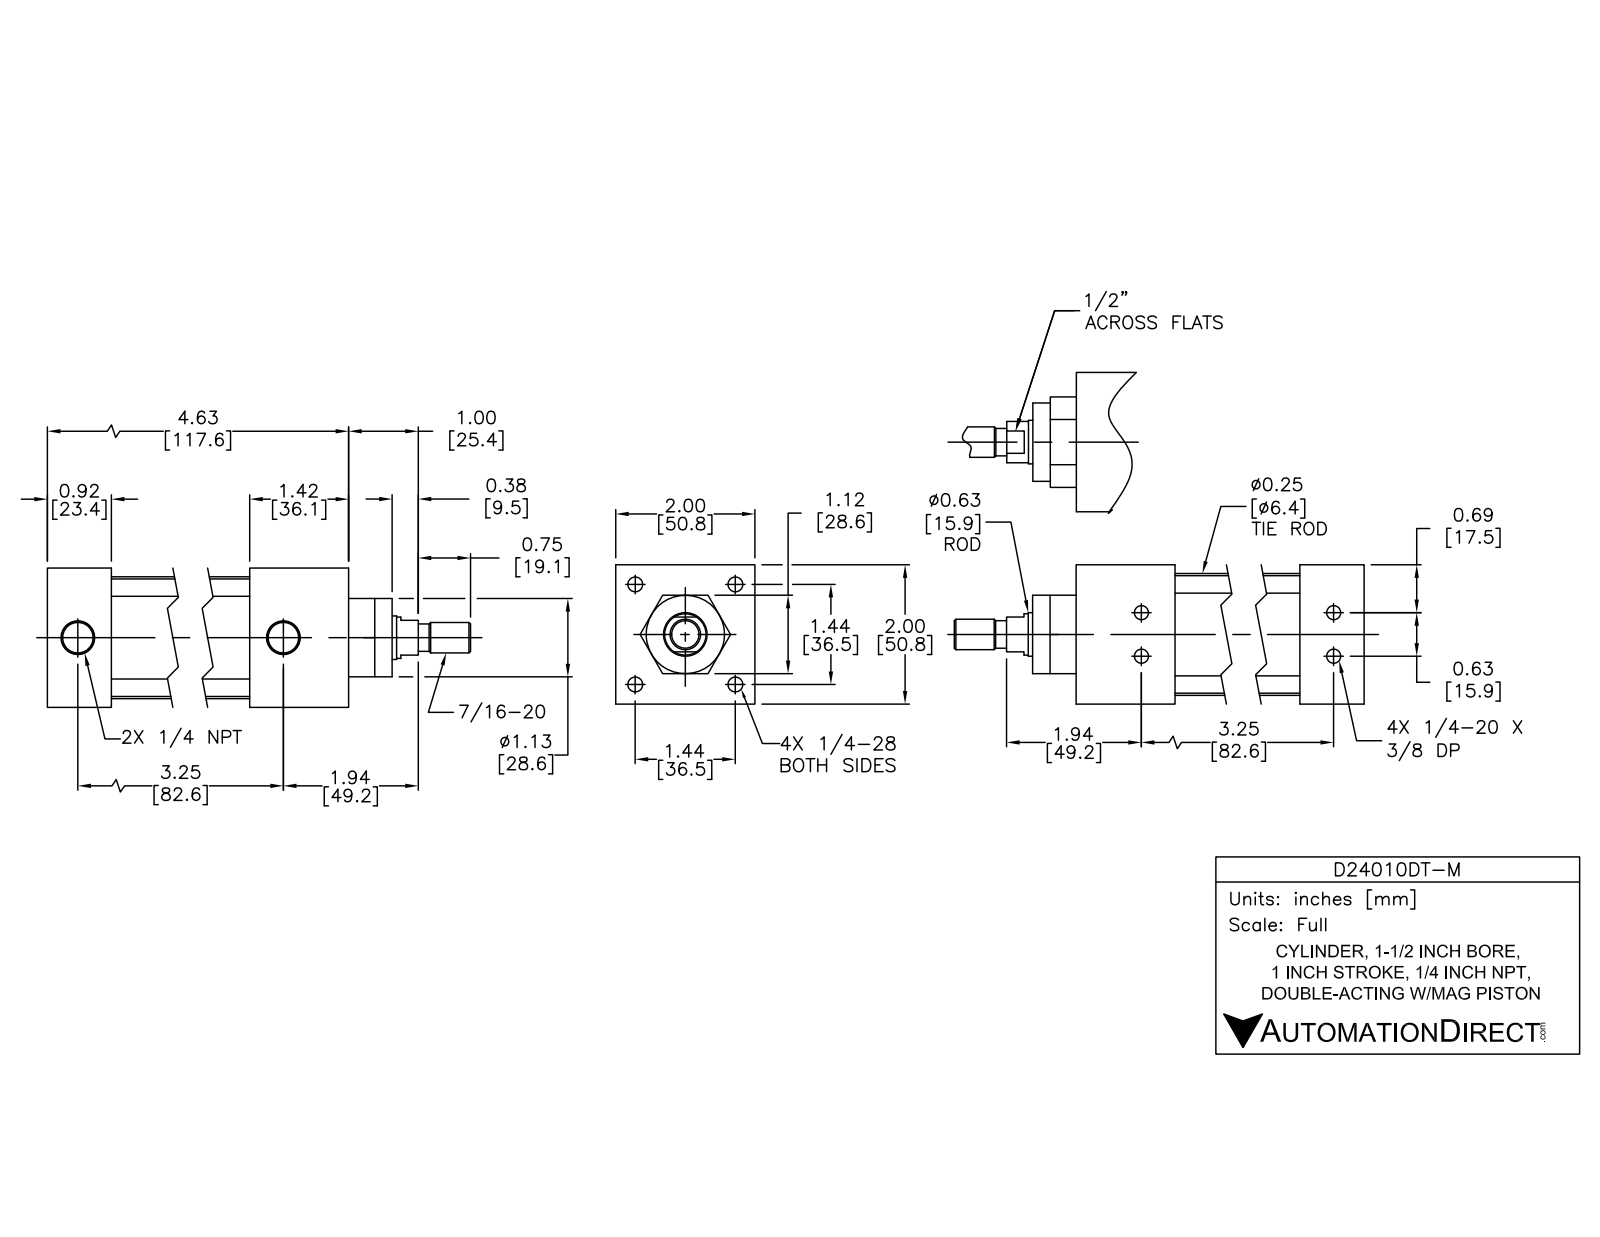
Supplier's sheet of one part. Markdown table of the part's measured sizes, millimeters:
| quantity | value |
| --- | --- |
| part name | D24010DT-M PISTON; D24010DT-M; D24010DT-M BODY |
| STEP written by | SolidWorks 2015 (AUTOMOTIVE_DESIGN) |
| units | millimeters |
| bodies | 12 solids, 303 faces (99 planar, 114 cylindrical, 90 other) |
| overall size | 161.8 × 50.8 × 50.8 |
| volume | 225 800 mm³ |
| surface area | 69 680 mm² |
| round holes (diameter × count) | 5 × 4, 5.4 × 4, 7.1 × 4, 10.3 × 4, 7.5 × 2, 12.1 × 2, 15.9 × 1, 16 × 1, 38.1 × 1 |
| round bosses / shafts (diameter × count) | 9.9 × 4, 6.4 × 4, 5.6 × 4, 44.5 × 1, 38 × 1, 28.5 × 1, 15.8 × 1, 15 × 1 |
| partial cylindrical surfaces (radius × count) | 5.1 × 4 |
| main face-to-face distances | 50.8, 117.4, 36.1, 81.3, 94, 57.9, 23.4, 28.5, 91.5, 55.4 |
| hole center spacings | 8, 25.8, 36.4, 15.9, 51.5, 82.5, 82.8, 82.8 |
